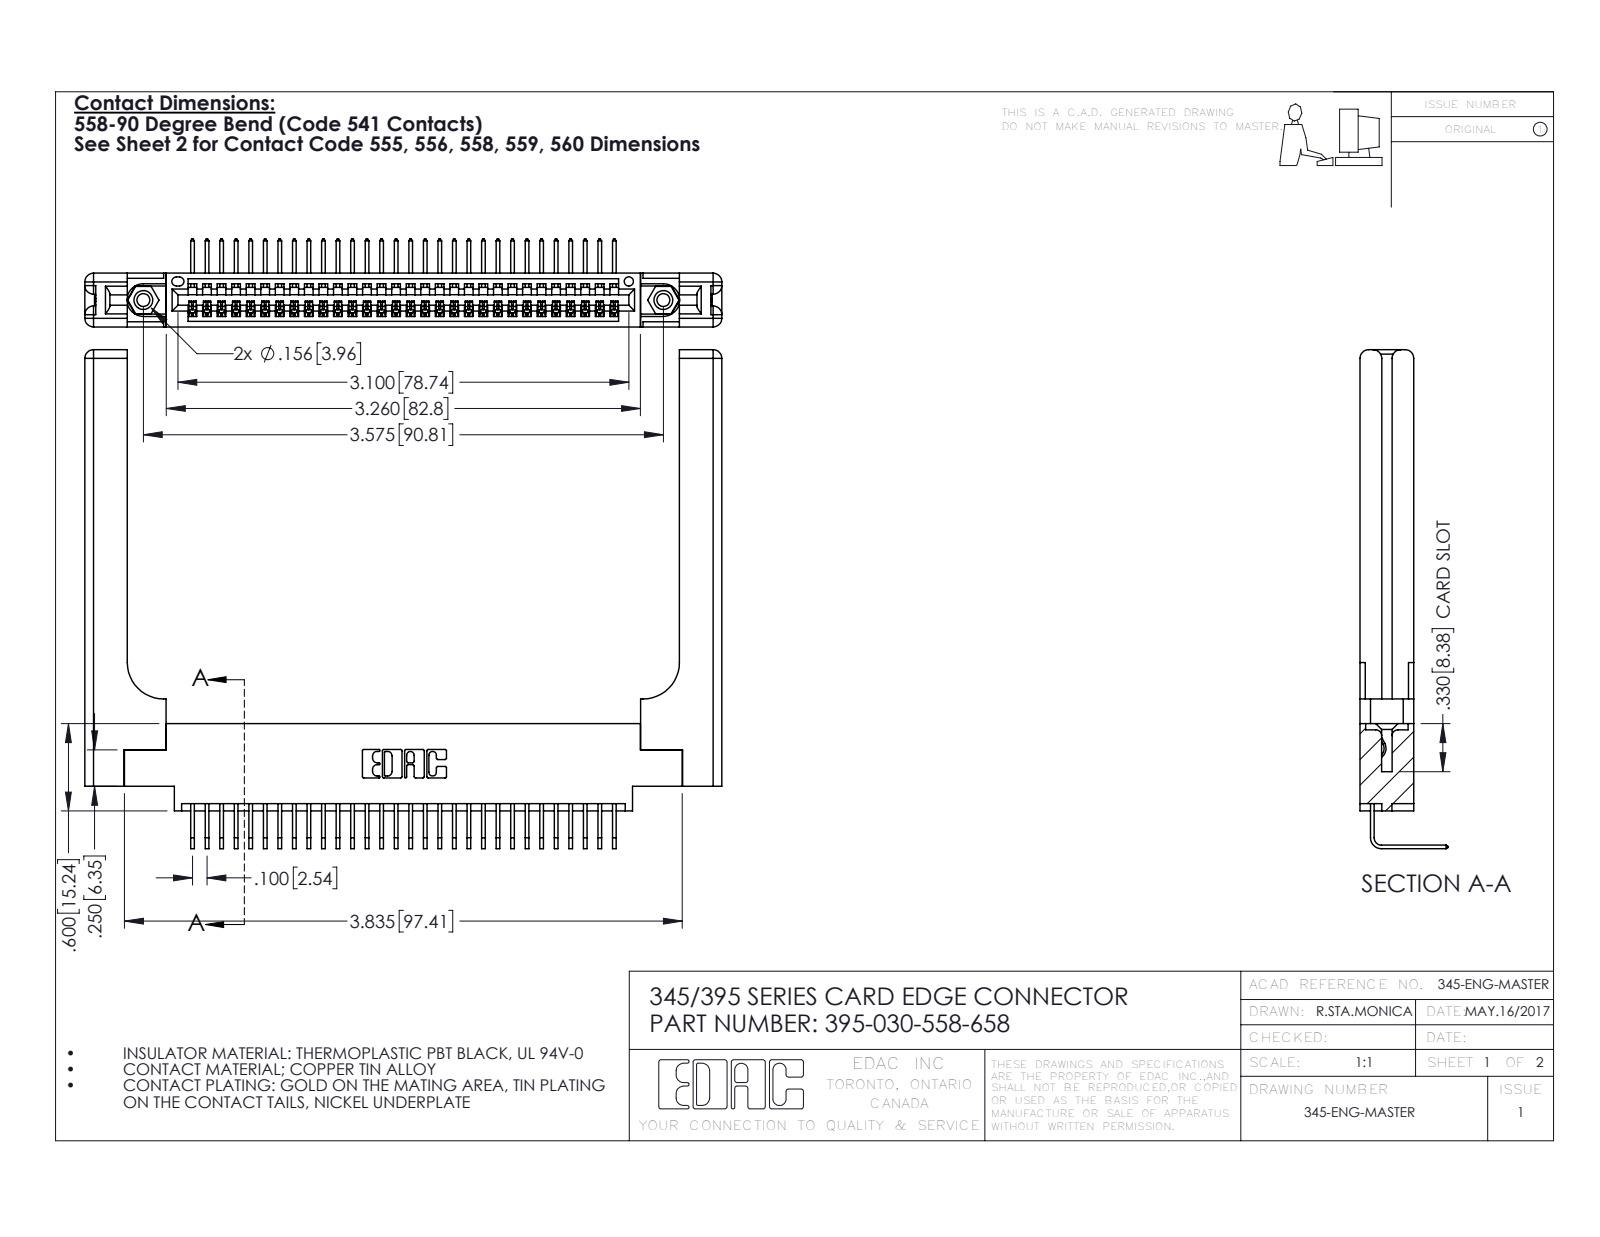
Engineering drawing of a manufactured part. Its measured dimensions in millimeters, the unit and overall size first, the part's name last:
Units: millimetres
Overall size (bounding box): 111.2 × 87.1 × 15.4
Round holes (diameter × count): ⌀2.3 ×2, ⌀3.2 ×2, ⌀4 ×2, ⌀1.6 ×1
Round bosses / shafts (diameter × count): ⌀3.9 ×2
Partial cylindrical surfaces — rounded edges, fillets, slot ends (radius × count): R0.2 ×60, R0.3 ×22, R1.5 ×16, R0.2 ×6, R0.8 ×6, R0.7 ×3, R0.8 ×2, R0.8 ×2
Main face-to-face distances: 9.4, 1.8, 7.6, 2.5, 6.9, 0.6, 5.1, 3.8, 3.8, 2
Hole centre spacings: 6.9, 84.8, 90.8
Volume: 18 960 mm³ · Surface area: 19 750 mm²
Bodies: 35 solids, 2186 faces (1492 planar, 634 cylindrical, 60 other)
Part name (STEP PRODUCT): 345-220-058_345-220-058; 345 Part_0.170 Offset - 0.156 Dia-TH; 395-030-558-658; 345-292-001_558 Tail - 2 (+1 more)
STEP written by: SolidWorks 2016 (CONFIG_CONTROL_DESIGN)
